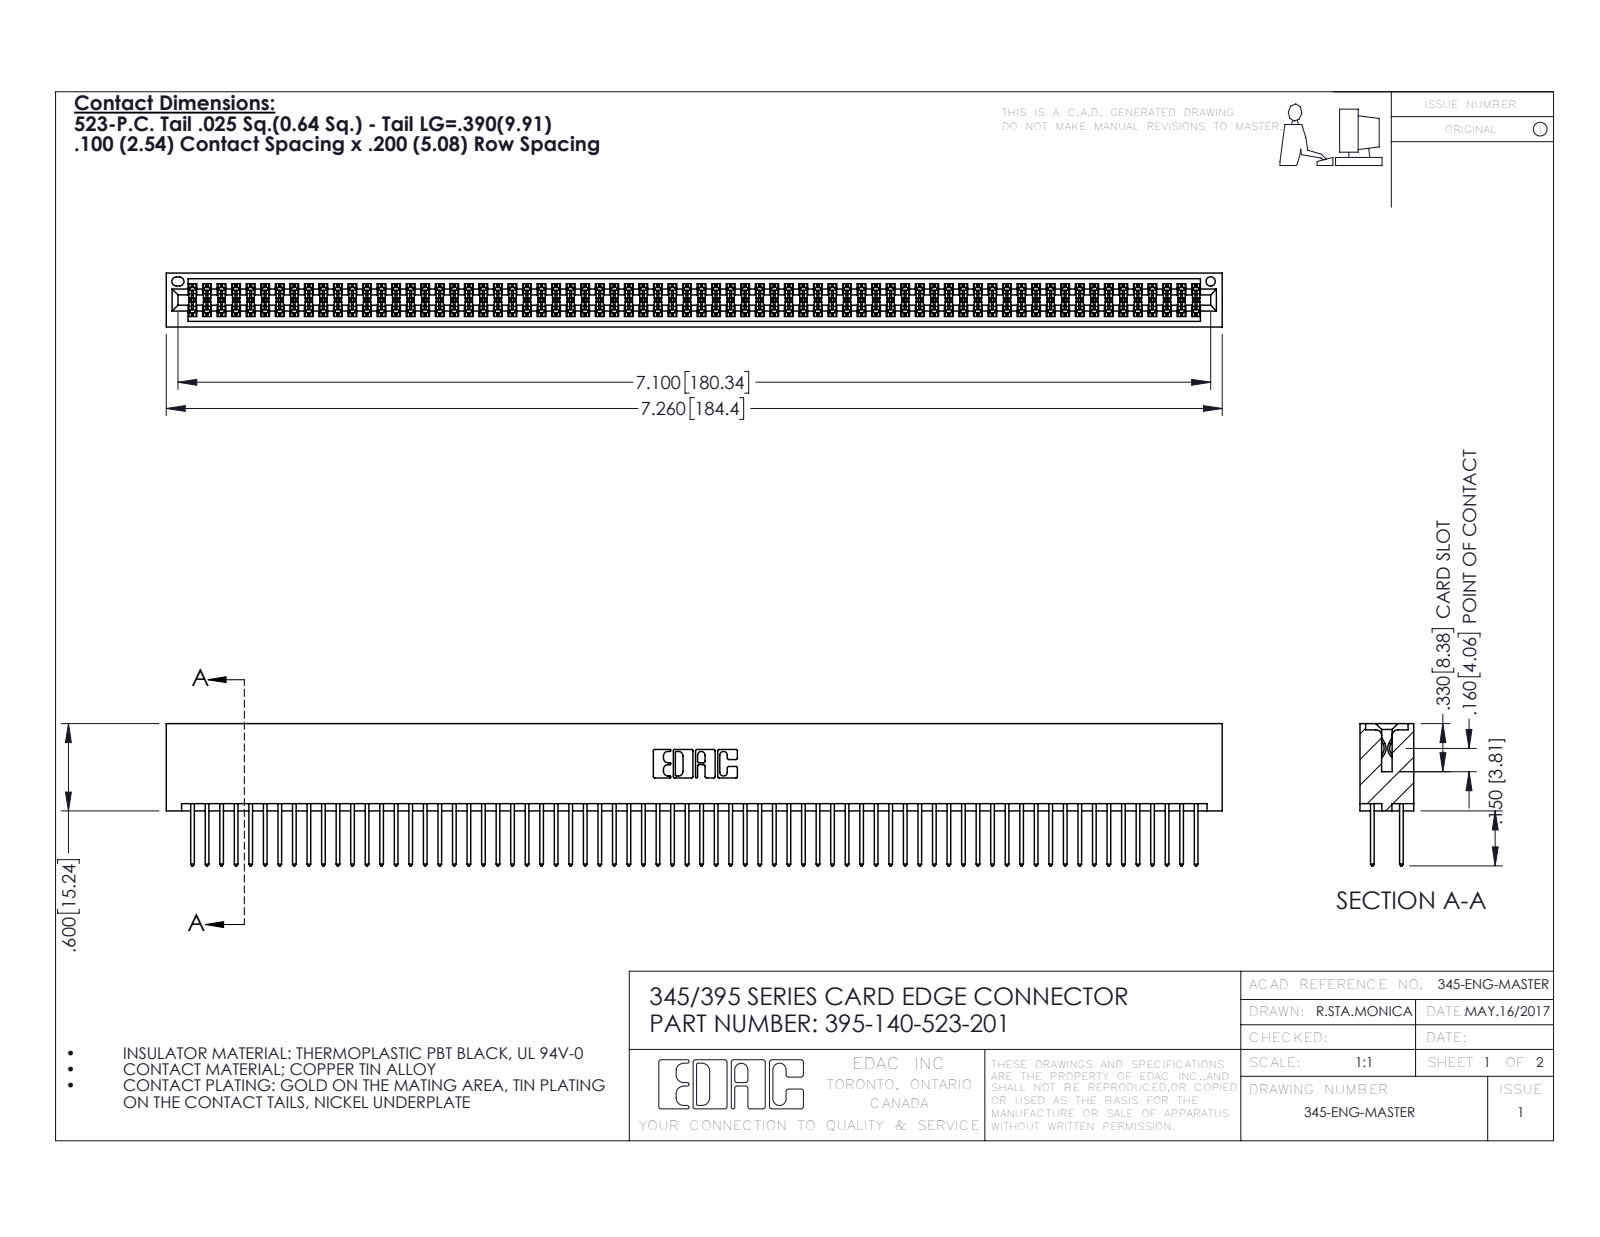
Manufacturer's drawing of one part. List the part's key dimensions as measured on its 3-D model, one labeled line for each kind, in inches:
Part name (STEP PRODUCT): 395-140-523-201; 345-292-001_345-293-123; 345 Part_No Mounting Lugs
STEP written by: SolidWorks 2016 (CONFIG_CONTROL_DESIGN)
Units: inches
Bodies: 141 solids, 7118 faces (4696 planar, 2422 cylindrical, 0 other)
Overall size (bounding box): 7.26 × 0.977 × 0.37
Volume: 1.164 in³ · Surface area: 47.01 in²
Round holes (diameter × count): ⌀0.064 ×1
Partial cylindrical surfaces — rounded edges, fillets, slot ends (radius × count): R0.006 ×210, R0.01 ×140, R0.01 ×22, R0.007 ×6, R0.031 ×6, R0.026 ×3, R0.014 ×2, R0.019 ×2
Main face-to-face distances: 0.298, 0.072, 0.2, 0.098, 0.272, 0.025, 0.37, 0.225, 0.175, 0.149
